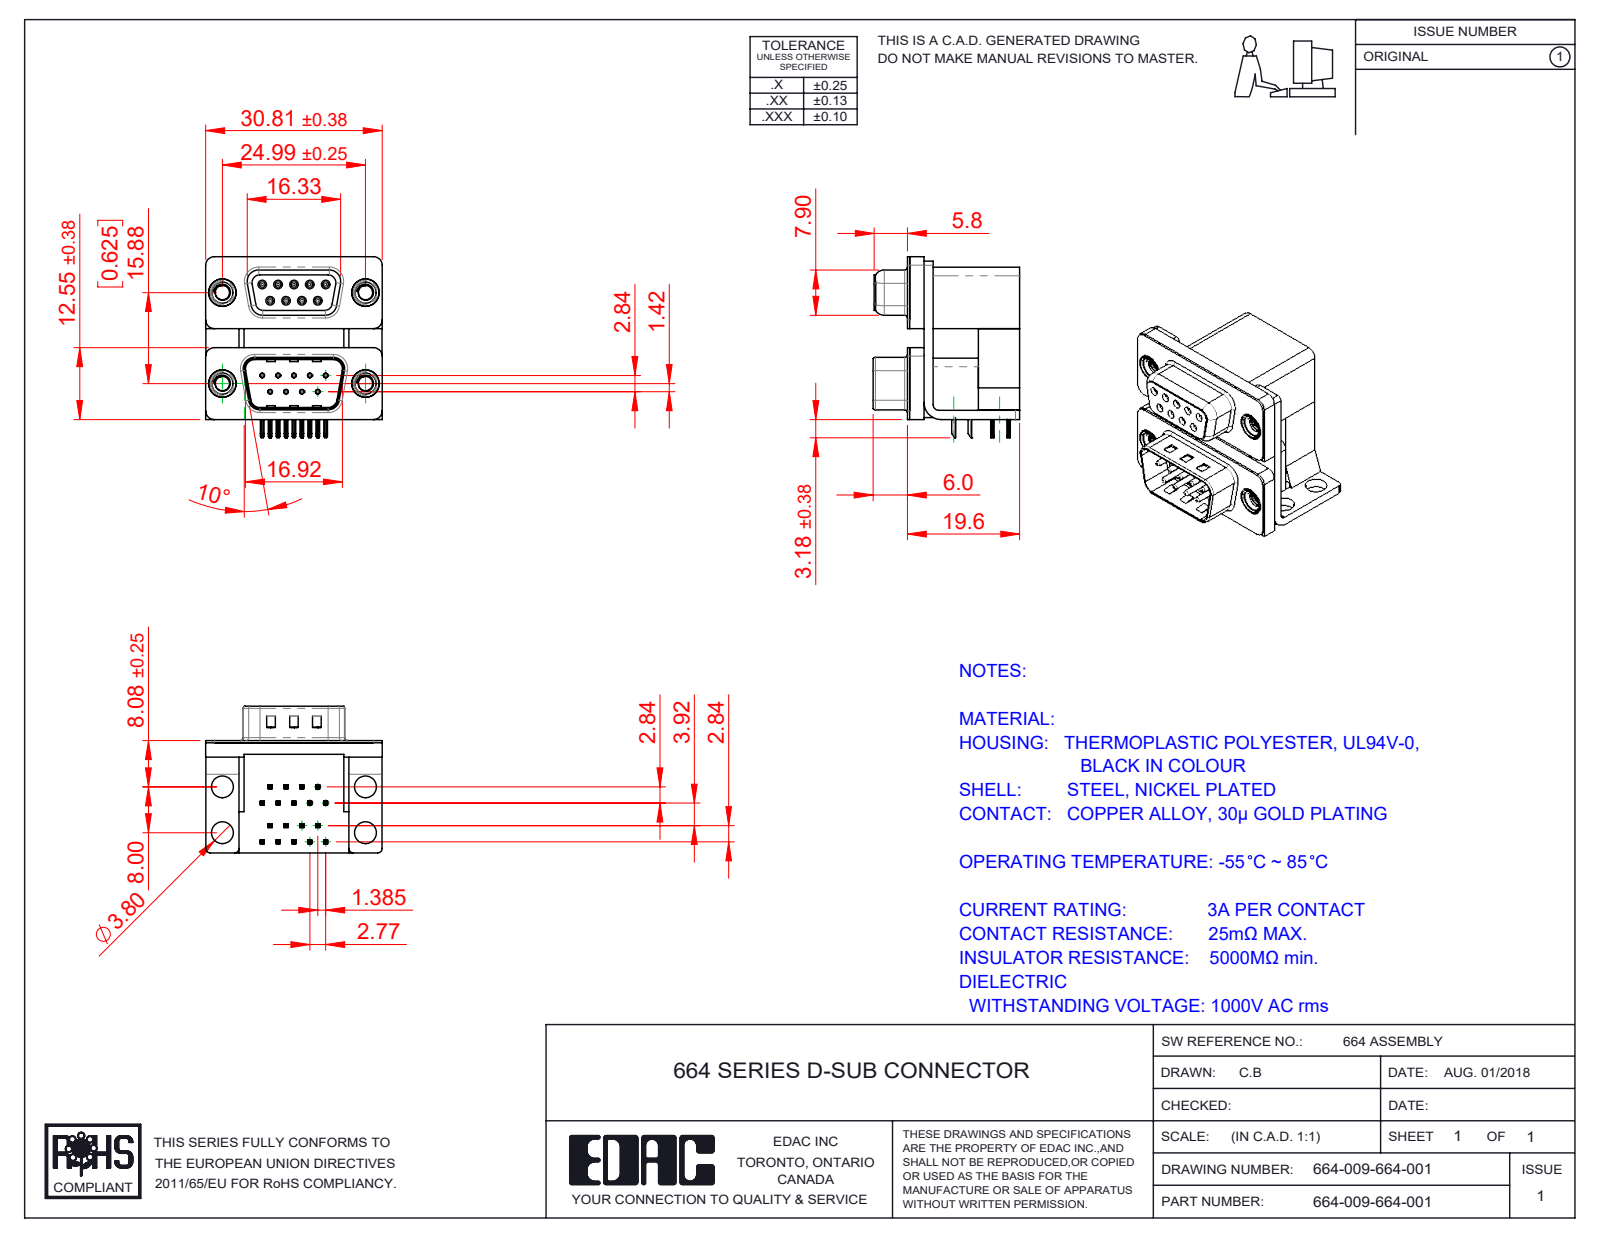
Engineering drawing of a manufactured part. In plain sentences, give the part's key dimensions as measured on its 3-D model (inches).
The part is named "664 Shell Receptacle_09 Contacts; 664 Mounting Bracket_NoneL; 664-009-664-001; 664 Housing Lower_09 Contacts (+8 more)". Its 3-D file was written by "SolidWorks 2020 (CONFIG_CONTROL_DESIGN)". It is 29 solids with 2533 faces: 1263 planar, 703 cylindrical and 567 other. Overall it measures 1.244 by 1.213 by 1.008 inches. Its volume is 0.628 cubic inches and its surface area 18.74 square inches. Round holes: 18 of diameter 0.031, 9 of diameter 0.014, 9 of diameter 0.035, 4 of diameter 0.098, 4 of diameter 0.138, 4 of diameter 0.15, 4 of diameter 0.157, 4 of diameter 0.189, 4 of diameter 0.197. Round bosses or shafts: 9 of diameter 0.047, 9 of diameter 0.03, 4 of diameter 0.193, 4 of diameter 0.187, 4 of diameter 0.154. Partial cylindrical surfaces (rounded edges, fillets, slot ends): 72 of radius 0.004, 36 of radius 0.006, 36 of radius 0.01, 18 of radius 0.005, 18 of radius 0.014, 13 of radius 0.059, 12 of radius 0.02, 10 of radius 0.053. The main face-to-face distances are 0.016, 0.098, 0.657, 0.756, 0.772, 0.114, 0.283, 0.374, 0.472, 0.488. The hole center spacings are 0.124, 0.109, 0.635, 0.625, 0.218, 0.662, 0.516, 0.739.
